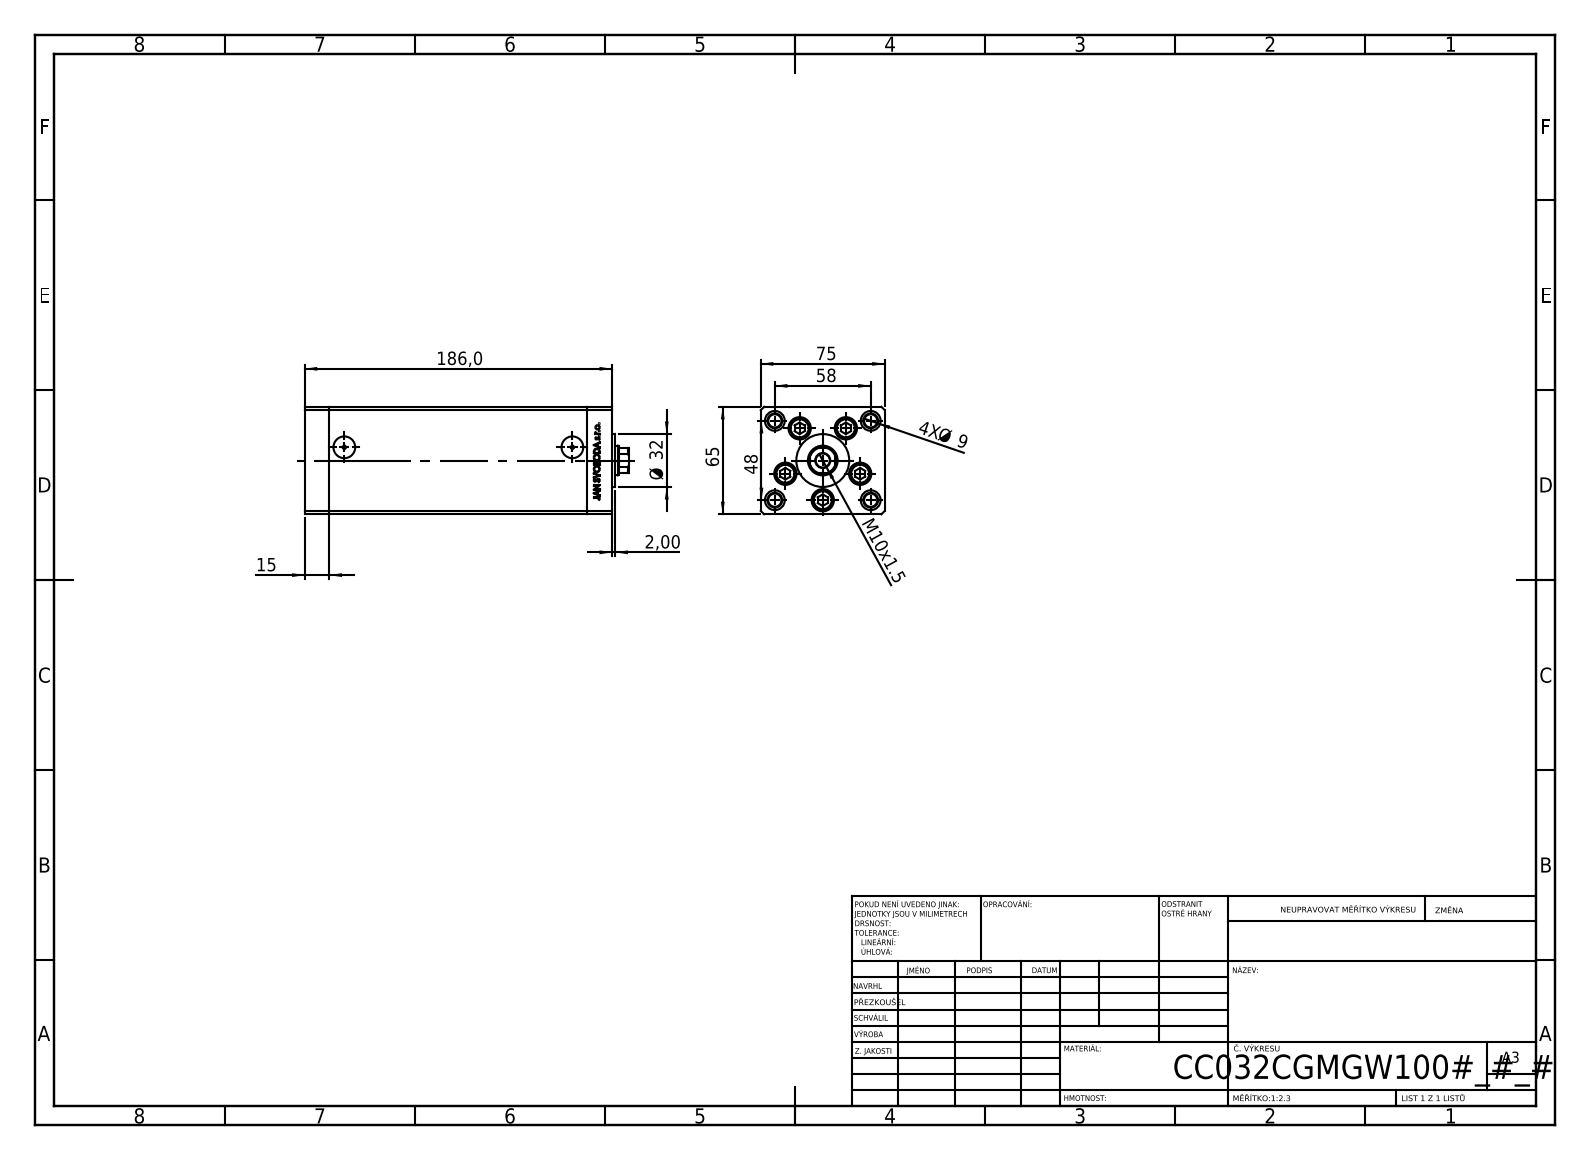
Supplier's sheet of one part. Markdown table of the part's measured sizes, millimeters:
| quantity | value |
| --- | --- |
| part name | V220C BACK_C; V220C_VC_C; V220C_C MIDDLE; ALLEN BOLT (+1 more) |
| STEP written by | SolidWorks 2019 (CONFIG_CONTROL_DESIGN) |
| units | millimeters |
| bodies | 13 solids, 1169 faces (540 planar, 167 cylindrical, 462 other) |
| overall size | 196 × 75 × 65 |
| volume | 757 889 mm³ |
| surface area | 153 912 mm² |
| round holes (diameter × count) | 9 × 9, 13.5 × 5, 8 × 4, 12 × 4, 2 × 2, 13.16 × 2, 8.5 × 1, 12.5 × 1, 18 × 1 |
| round bosses / shafts (diameter × count) | 8 × 5, 12.5 × 4, 32 × 1 |
| partial cylindrical surfaces (radius × count) | 0.93 × 2, 8.5 × 1 |
| main face-to-face distances | 75, 65, 15, 156, 171, 186, 28, 54.5, 10.5, 26.25 |
| hole center spacings | 24, 37.64, 15.67, 17.22, 27.71, 28.83, 29, 32.63 |
